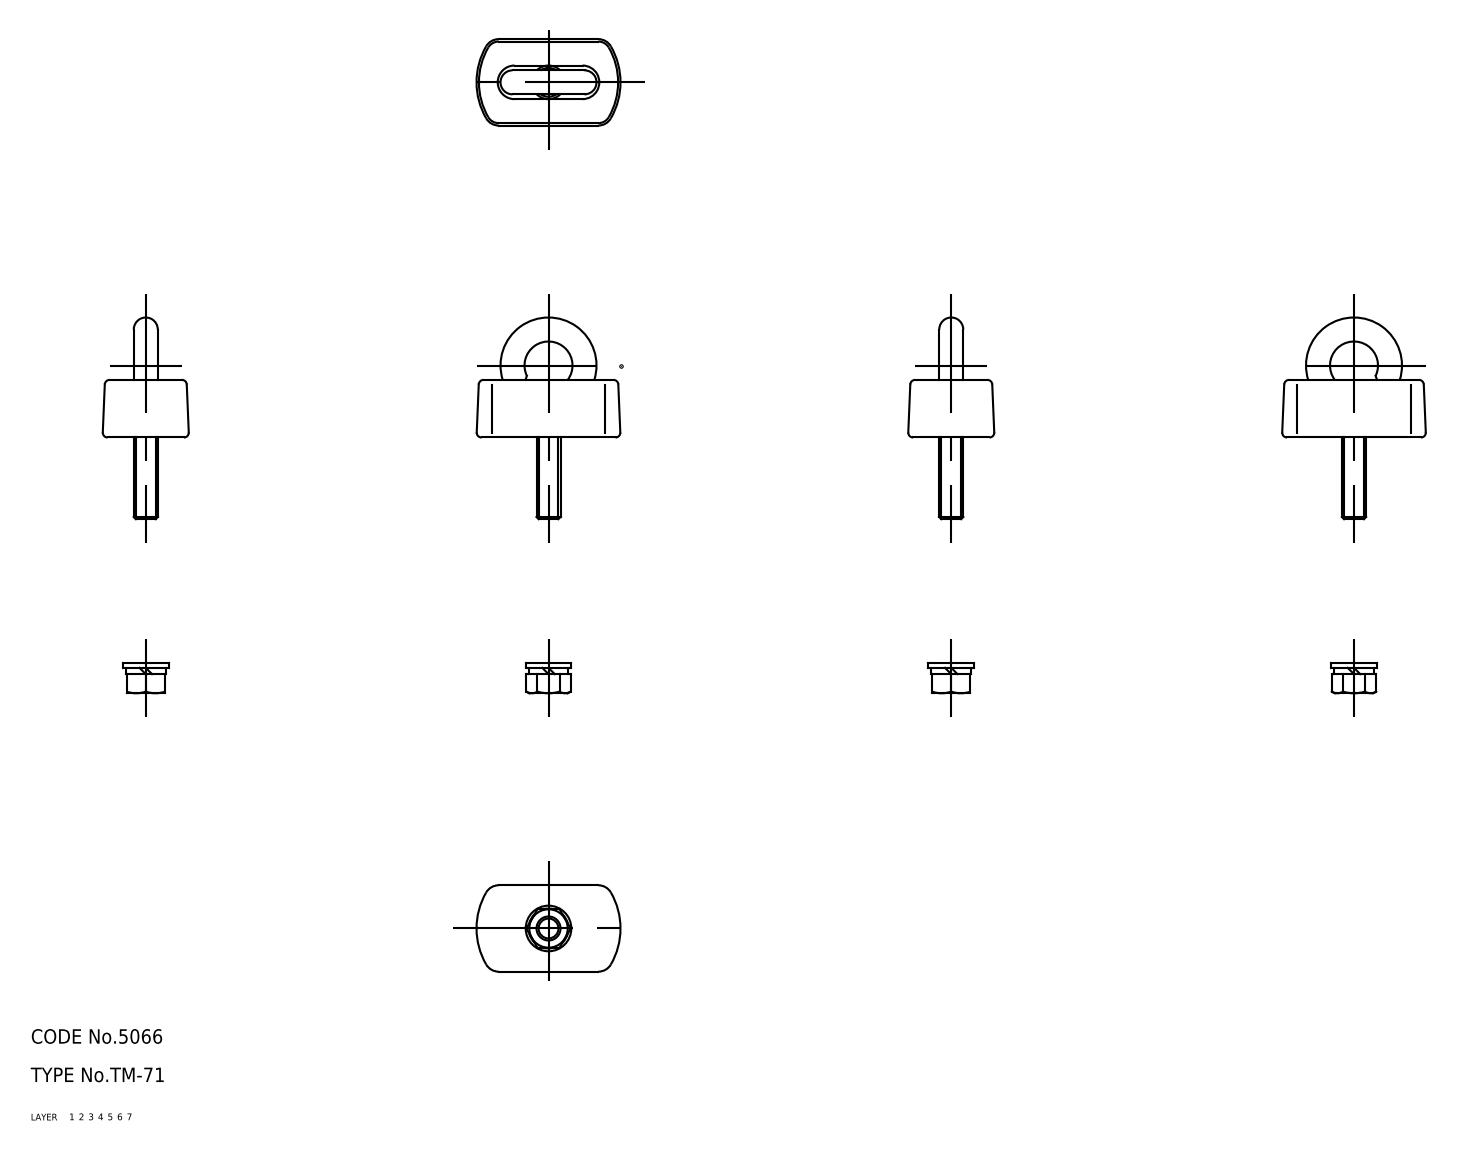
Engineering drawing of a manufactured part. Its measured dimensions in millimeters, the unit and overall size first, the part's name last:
Units: millimetres
Overall size (bounding box): 42 × 30 × 18
Volume: 6 519 mm³ · Surface area: 3 751 mm²
Bodies: 5 solids, 57 faces (0 planar, 0 cylindrical, 57 other)
Part name (STEP PRODUCT): nut; washer_B; washer_A; stopper (+2 more)
STEP written by: CADfix (AUTOMOTIVE_DESIGN)
